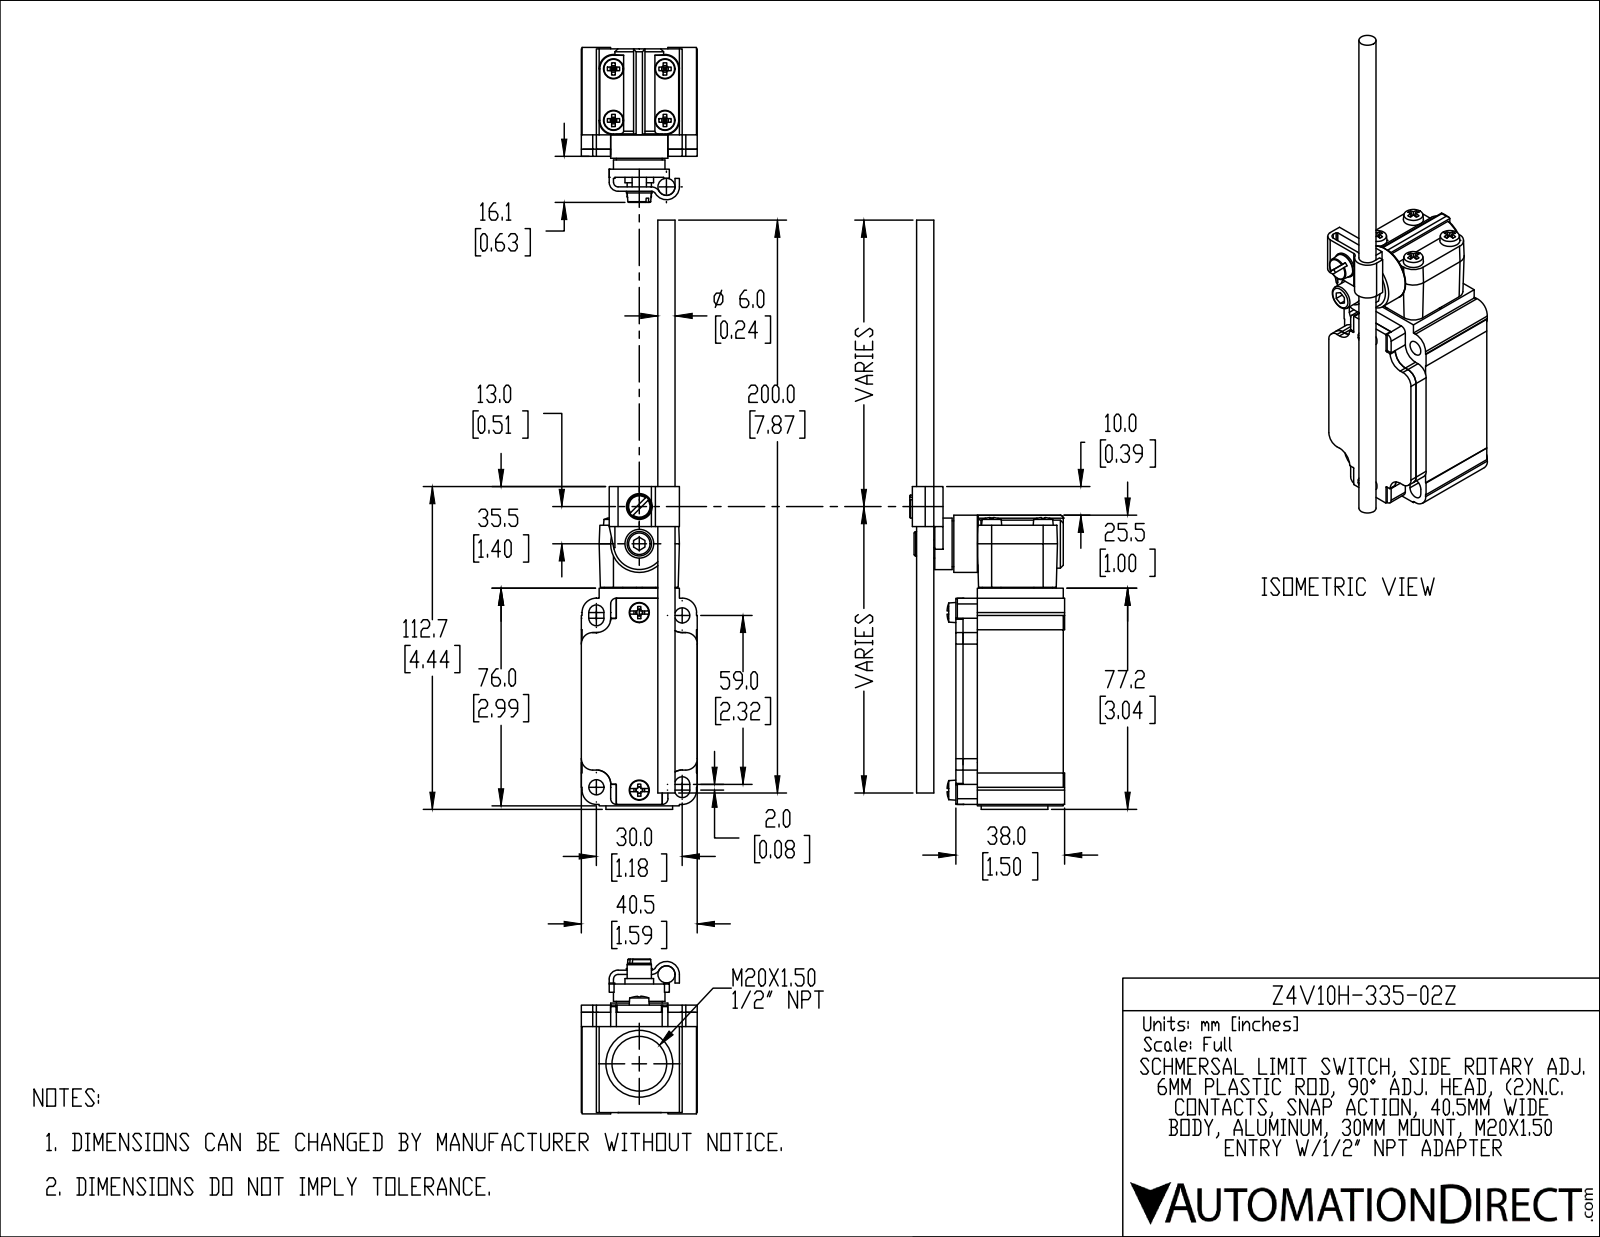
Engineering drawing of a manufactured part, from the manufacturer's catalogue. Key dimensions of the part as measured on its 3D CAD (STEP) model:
Part name (STEP PRODUCT): Z4V10H-335-02Z
STEP written by: SolidWorks 2019 (CONFIG_CONTROL_DESIGN)
Units: inches
Bodies: 8 solids, 513 faces (332 planar, 130 cylindrical, 51 other)
Overall size (bounding box): 8.098 × 2.13 × 1.594
Volume: 8.097 in³ · Surface area: 59.63 in²
Round holes (diameter × count): ⌀0.081 ×4, ⌀0.209 ×2, ⌀0.236 ×1, ⌀0.711 ×1, ⌀0.75 ×1
Round bosses / shafts (diameter × count): ⌀0.709 ×2, ⌀0.079 ×2, ⌀0.917 ×1, ⌀0.787 ×1, ⌀0.669 ×1, ⌀0.63 ×1, ⌀0.394 ×1, ⌀0.354 ×1
Partial cylindrical surfaces — rounded edges, fillets, slot ends (radius × count): R0.01 ×12, R0.157 ×12, R0.197 ×12, R0.079 ×4, R0.104 ×4, R0.128 ×4, R0.197 ×4, R0.039 ×2
Main face-to-face distances: 0.197, 1.181, 1.378, 0.098, 1.476, 0.295, 1.594, 0.02, 0.472, 0.177
Hole centre spacings: 0.492, 0.696, 0.494, 0.984, 0.039, 0.453, 0.531, 0.861
